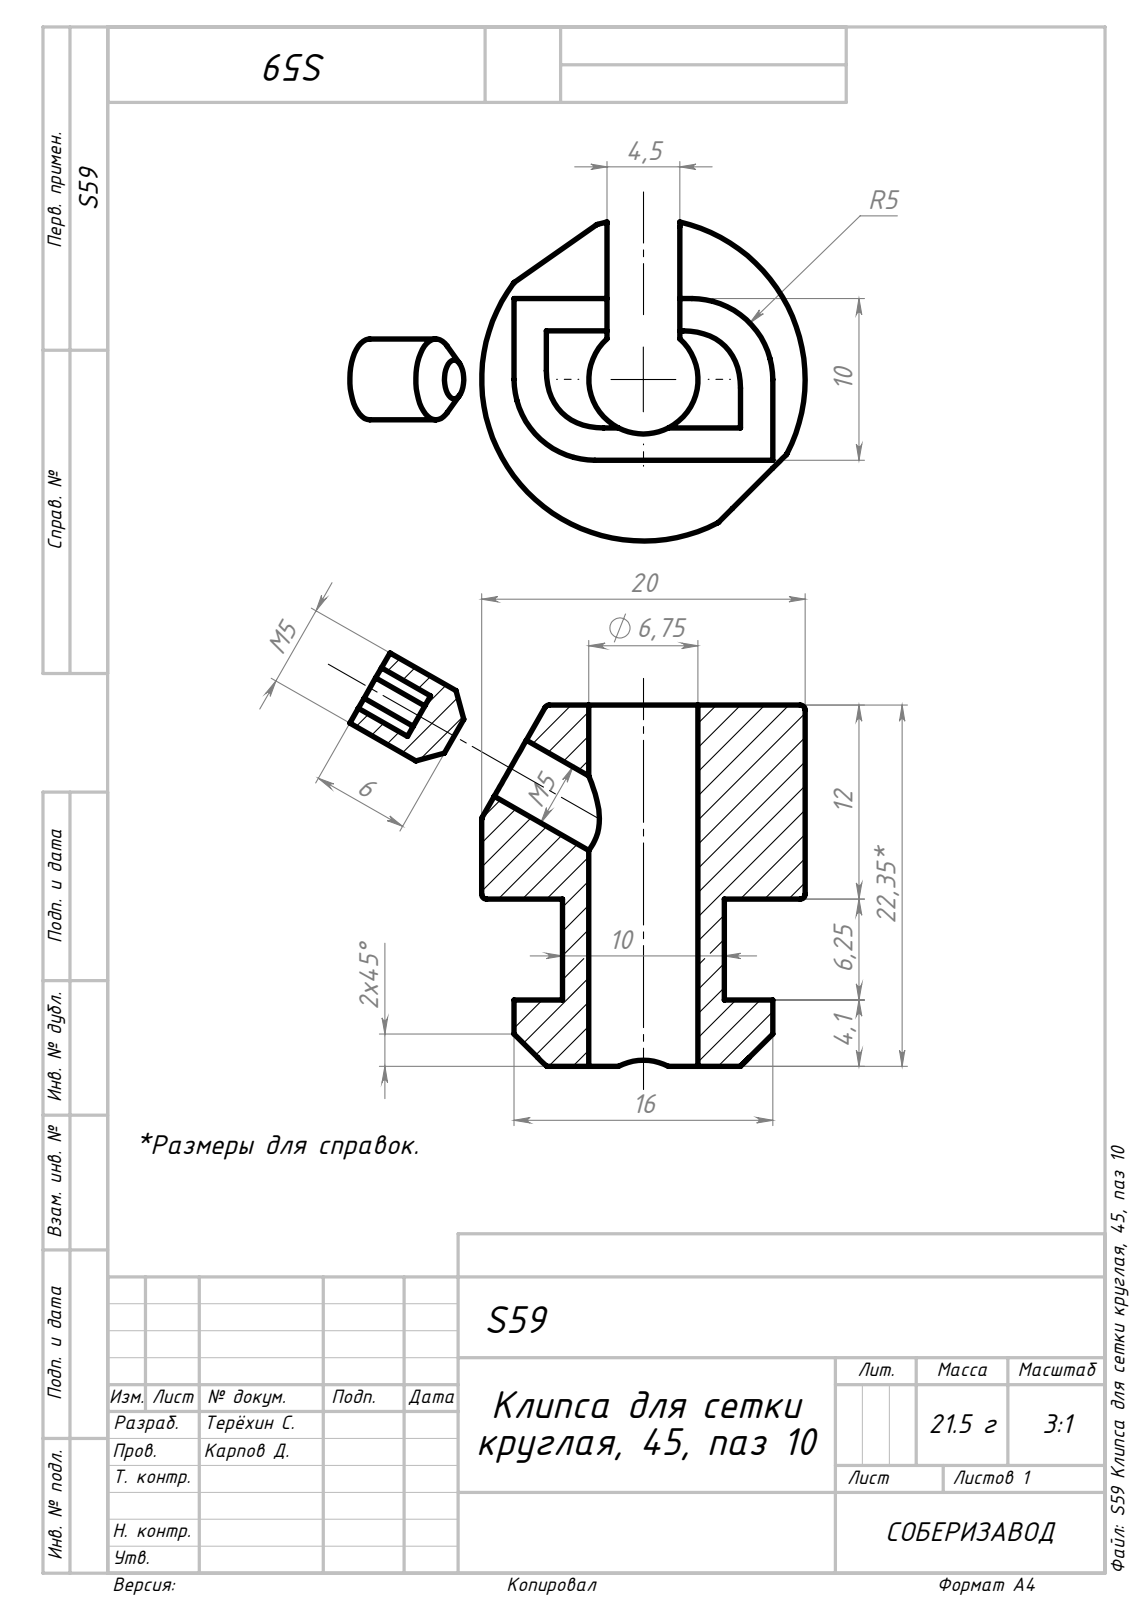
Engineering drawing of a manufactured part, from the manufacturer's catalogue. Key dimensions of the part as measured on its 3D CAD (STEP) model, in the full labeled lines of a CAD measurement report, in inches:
Part name (STEP PRODUCT): S59 Клипса для сетки круглая, 45, паз 10_2; S59 Винт установочный; S59; S59 Клипса
STEP written by: SolidWorks 2021 (AUTOMOTIVE_DESIGN)
Units: inches
Bodies: 2 solids, 67 faces (32 planar, 23 cylindrical, 12 other)
Overall size (bounding box): 1.109 × 1.007 × 0.777
Volume: 0.211 in³ · Surface area: 3.636 in²
Round holes (diameter × count): ⌀0.157 ×1
Round bosses / shafts (diameter × count): ⌀0.197 ×1
Partial cylindrical surfaces — rounded edges, fillets, slot ends (radius × count): R0.012 ×8, R0.197 ×5, R0.133 ×1, R0.394 ×1
Main face-to-face distances: 0.472, 0.177, 0.394, 0.246, 0.108, 0.285, 0.719, 0.161, 0.407, 0.88
